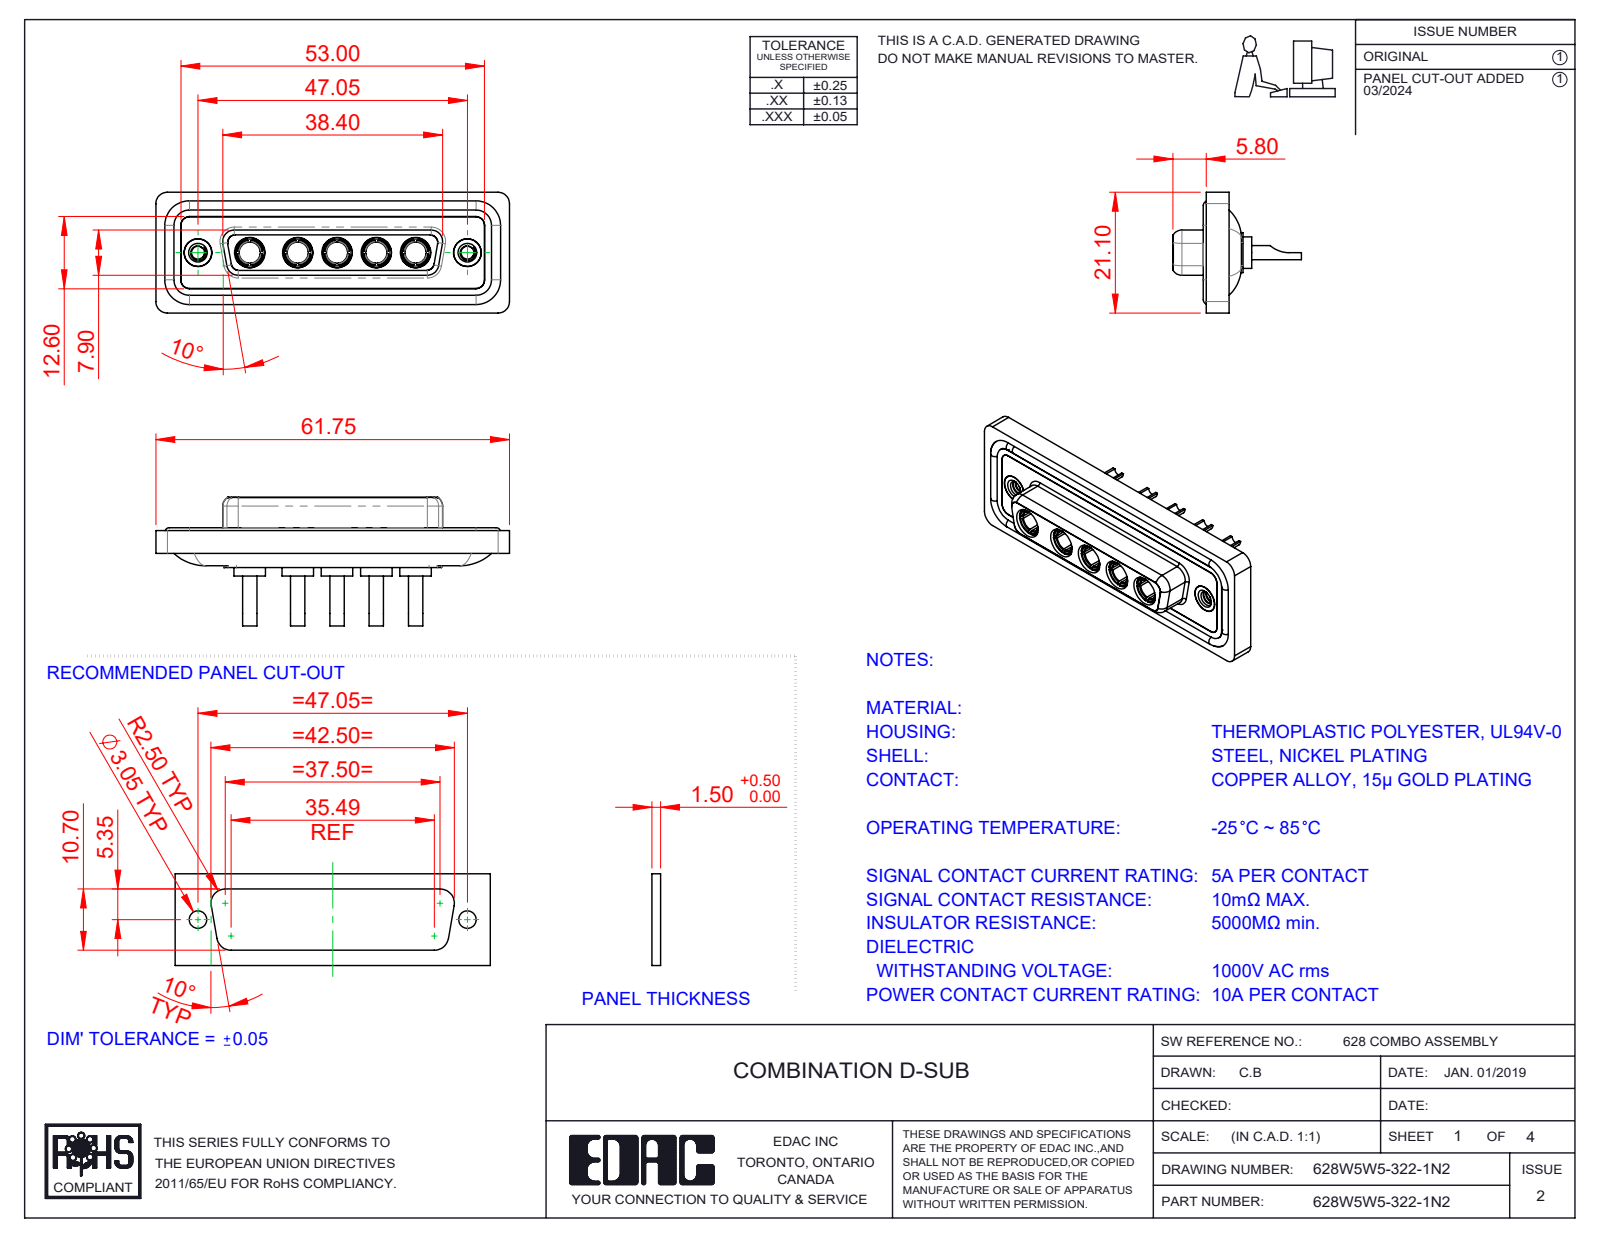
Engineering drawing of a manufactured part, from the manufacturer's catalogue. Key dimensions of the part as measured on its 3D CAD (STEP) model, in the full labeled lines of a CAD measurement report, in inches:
Part name (STEP PRODUCT): 628Combo Waterproof Housing_25 Contacts; 628W5W5-322-1N2; 628Combo Threaded Rivet_2; 628Combo Shell Front_25 Contacts (+3 more)
STEP written by: SolidWorks 2023 (CONFIG_CONTROL_DESIGN)
Units: inches
Bodies: 17 solids, 781 faces (260 planar, 318 cylindrical, 203 other)
Overall size (bounding box): 2.431 × 0.884 × 0.831
Volume: 0.498 in³ · Surface area: 21.16 in²
Round holes (diameter × count): ⌀0.191 ×7, ⌀0.067 ×5, ⌀0.146 ×5, ⌀0.209 ×5, ⌀0.089 ×2, ⌀0.157 ×2, ⌀0.159 ×2, ⌀0.197 ×2
Round bosses / shafts (diameter × count): ⌀0.217 ×5, ⌀0.205 ×5, ⌀0.195 ×5, ⌀0.187 ×5, ⌀0.148 ×5, ⌀0.098 ×5, ⌀0.063 ×4, ⌀0.195 ×2
Partial cylindrical surfaces — rounded edges, fillets, slot ends (radius × count): R0.059 ×22, R0.079 ×18, R0.053 ×8, R0.063 ×8, R0.083 ×5, R0.01 ×4, R0.02 ×4, R0.024 ×4
Main face-to-face distances: 0.016, 0.071, 0.293, 0.222, 0.02, 0.278, 0.26, 0.063, 0.043, 0.114
Hole centre spacings: 0.27, 0.356, 0.54, 1.496, 0.33, 0.6, 0.626, 0.686
